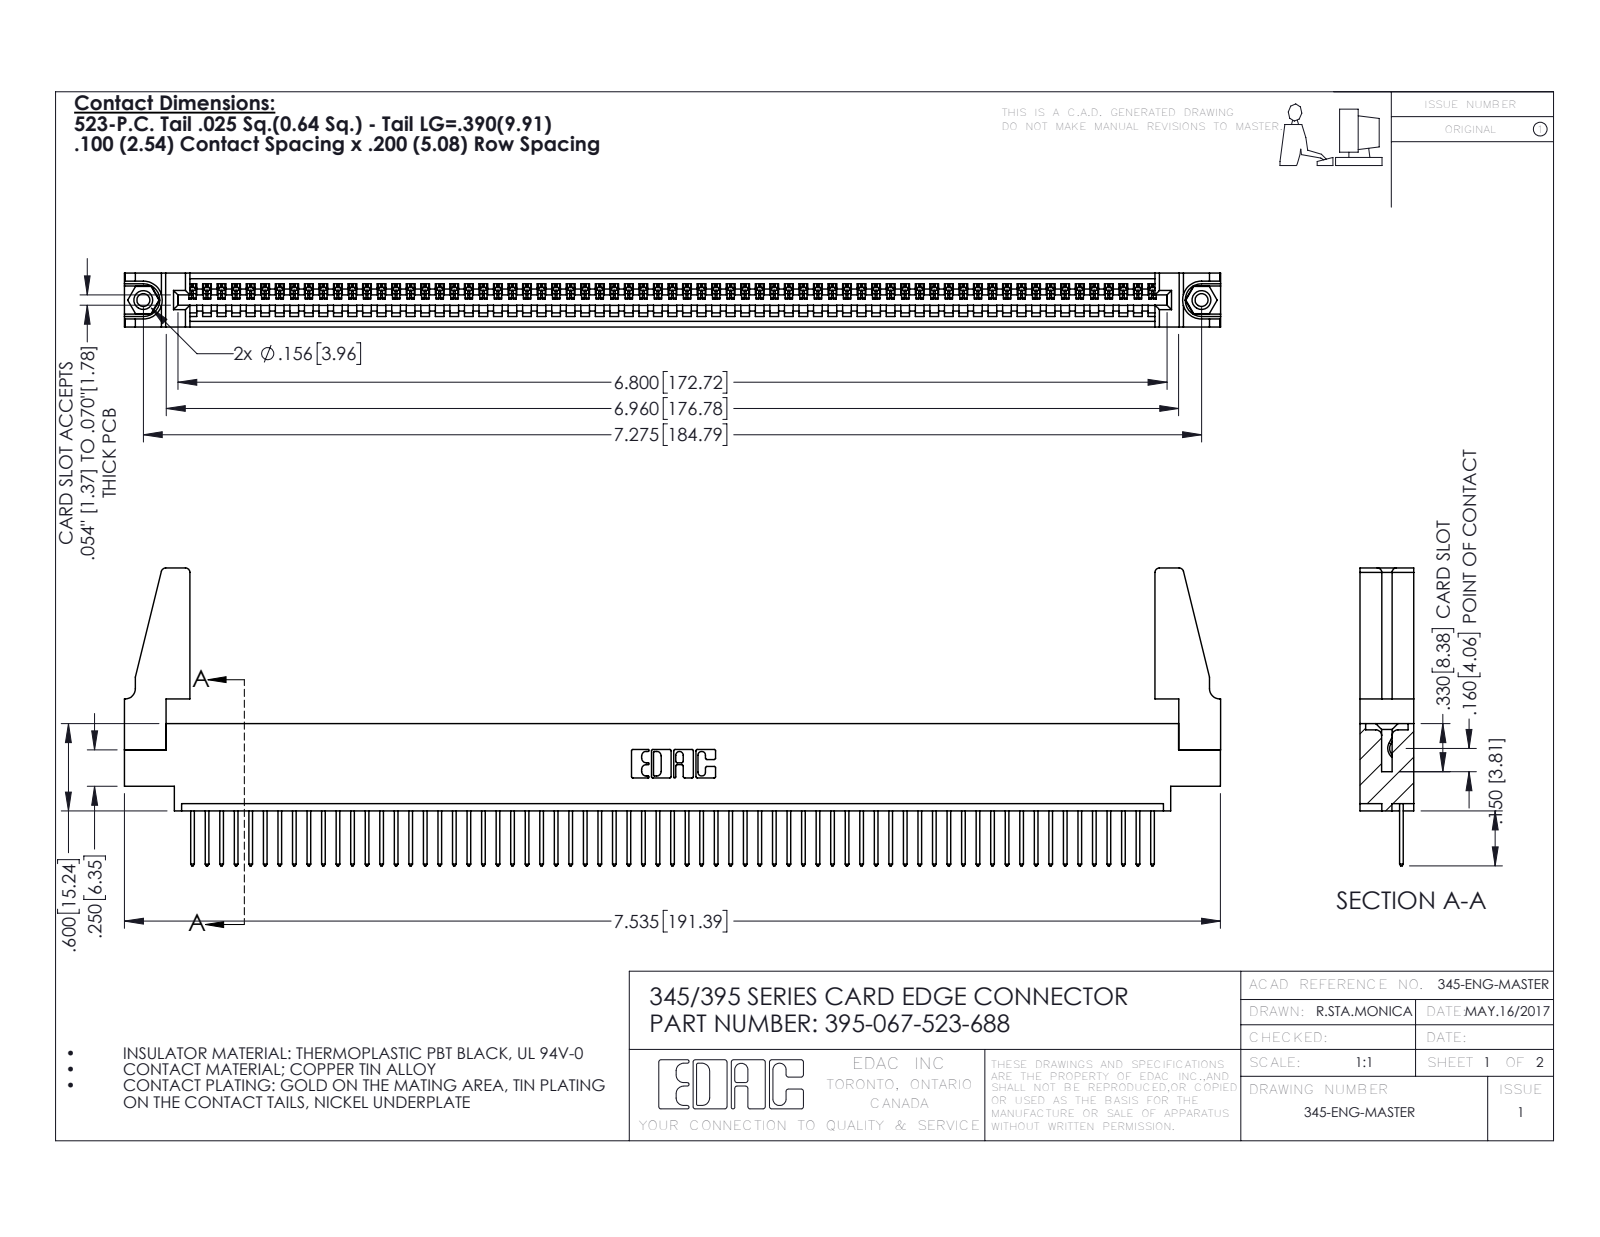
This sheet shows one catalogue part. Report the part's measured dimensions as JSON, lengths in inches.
{"part_name": "345-220-078_345-220-088; 345-250-001_345-250-001-102; 345-292-001_345-293-123; 345 Part_0.170 Offset - 0.156 Dia-TH (+1 more)", "step_written_by": "SolidWorks 2016 (CONFIG_CONTROL_DESIGN)", "units": "inches", "bodies": {"solids": 72, "faces": 4140, "planar": 2836, "cylindrical": 1288, "other": 16}, "overall_size": [7.536, 2.047, 0.37], "volume_in3": 1.312, "surface_area_in2": 43.27, "round_holes": [[0.089, 2], [0.125, 2], [0.156, 2], [0.064, 1]], "round_bosses_or_shafts": [[0.155, 2]], "partial_cylinders_radius": [[0.006, 134], [0.01, 134], [0.01, 22], [0.03, 8], [0.007, 6], [0.031, 6], [0.026, 3], [0.031, 2]], "face_to_face_distances": [0.072, 0.298, 0.37, 0.098, 0.272, 0.025, 0.2, 0.225, 0.175, 0.149], "hole_center_spacings": [0.27, 7.039, 7.275]}
